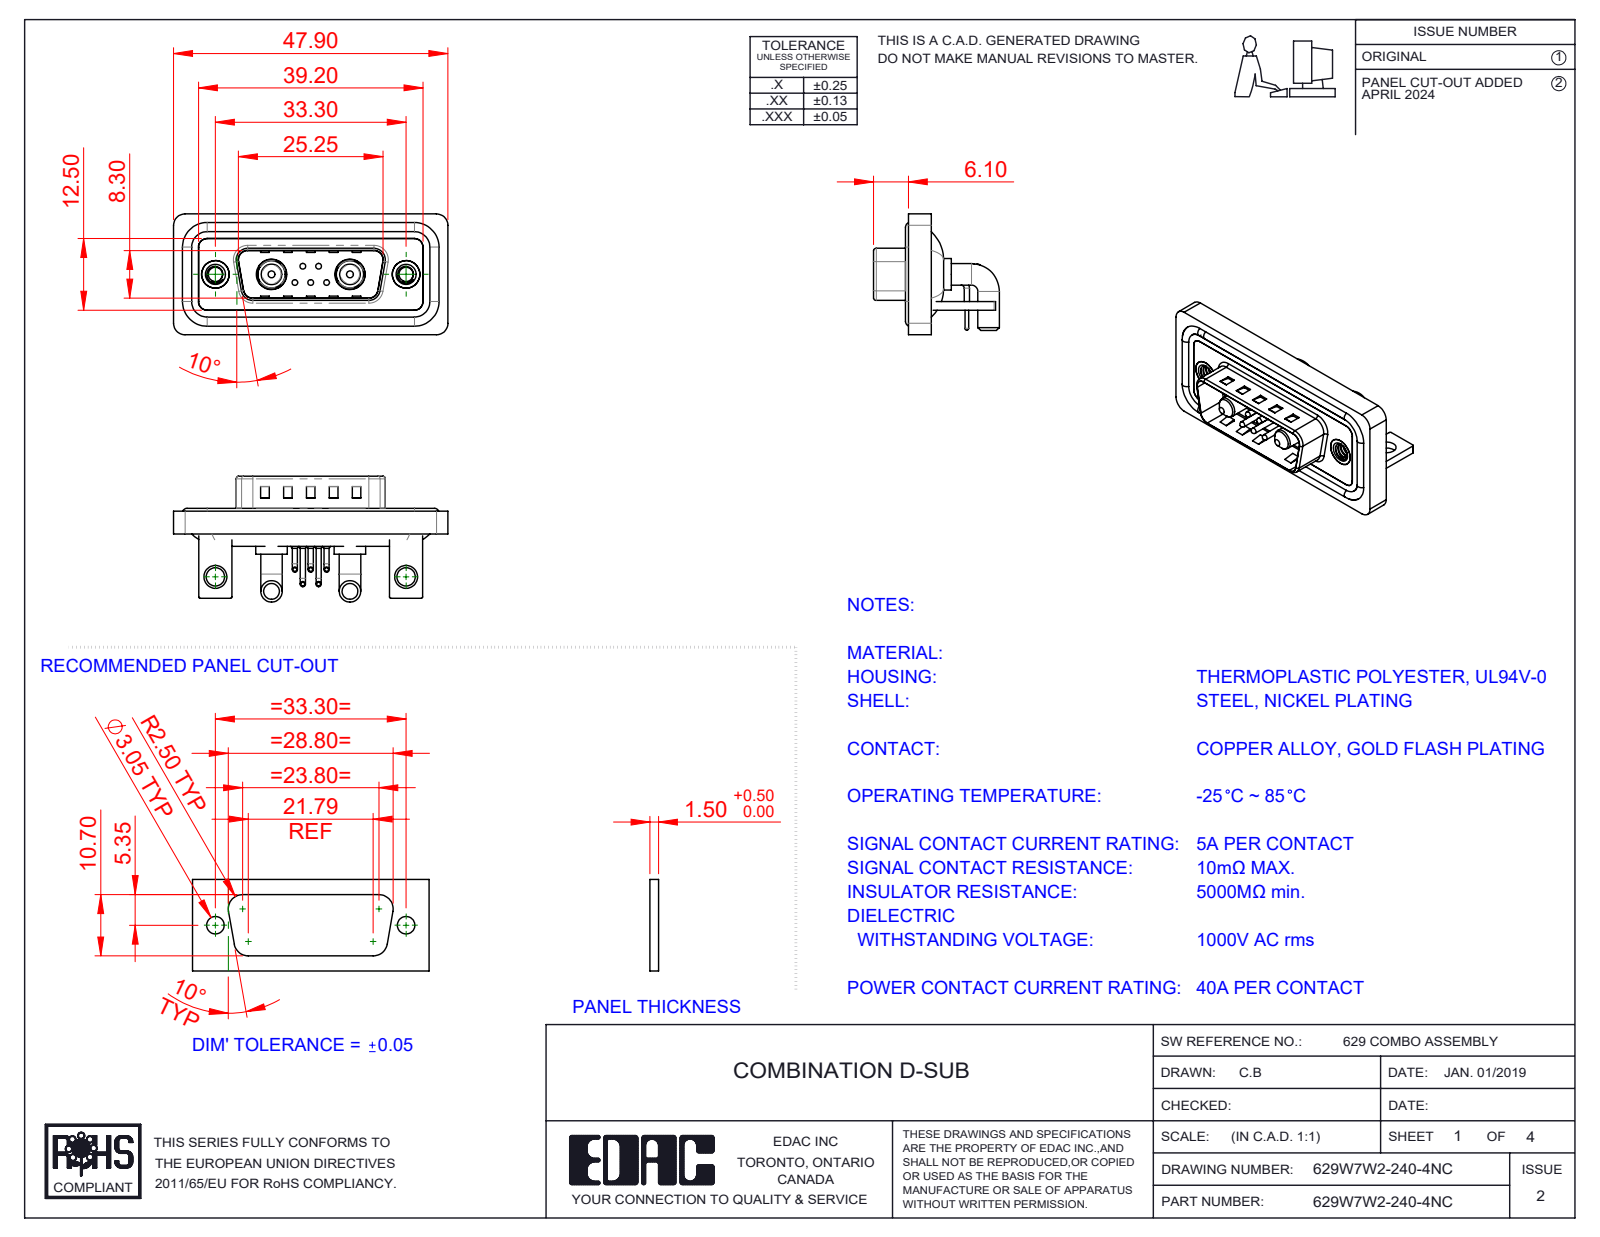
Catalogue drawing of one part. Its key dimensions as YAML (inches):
part_name: "629Combo Stabilizer Bracket; 629Combo Shell Front_15 Contacts; 629Combo Shell Rear_15 Contacts; 629Combo Contact Row 1 (+6 more)"
step_written_by: "SolidWorks 2023 (CONFIG_CONTROL_DESIGN)"
units: inches
bodies: {solids: 18, faces: 1121, planar: 537, cylindrical: 424, other: 160}
overall_size: [1.886, 0.865, 0.831]
volume: 0.372
surface_area: 15.22
round_holes:
  - {diameter: 0.03, count: 5}
  - {diameter: 0.063, count: 5}
  - {diameter: 0.079, count: 5}
  - {diameter: 0.098, count: 2}
  - {diameter: 0.126, count: 2}
  - {diameter: 0.157, count: 2}
  - {diameter: 0.189, count: 2}
  - {diameter: 0.191, count: 2}
  - {diameter: 0.197, count: 2}
  - {diameter: 0.209, count: 2}
round_bosses_or_shafts:
  - {diameter: 0.035, count: 10}
  - {diameter: 0.059, count: 5}
  - {diameter: 0.039, count: 5}
  - {diameter: 0.026, count: 5}
  - {diameter: 0.148, count: 4}
  - {diameter: 0.063, count: 4}
  - {diameter: 0.217, count: 2}
  - {diameter: 0.205, count: 2}
partial_cylinders:
  - {radius: 0.079, count: 21}
  - {radius: 0.059, count: 18}
  - {radius: 0.01, count: 16}
  - {radius: 0.02, count: 9}
  - {radius: 0.063, count: 8}
  - {radius: 0.04, count: 5}
  - {radius: 0.024, count: 4}
  - {radius: 0.026, count: 4}
face_to_face_distances: [0.016, 0.059, 0.031, 0.114, 0.083, 0.043, 0.063, 0.047, 0.146, 0.177]
hole_center_spacings: [0.124, 0.109, 0.386, 0.925, 1.311, 0.17, 0.17, 0.198]
